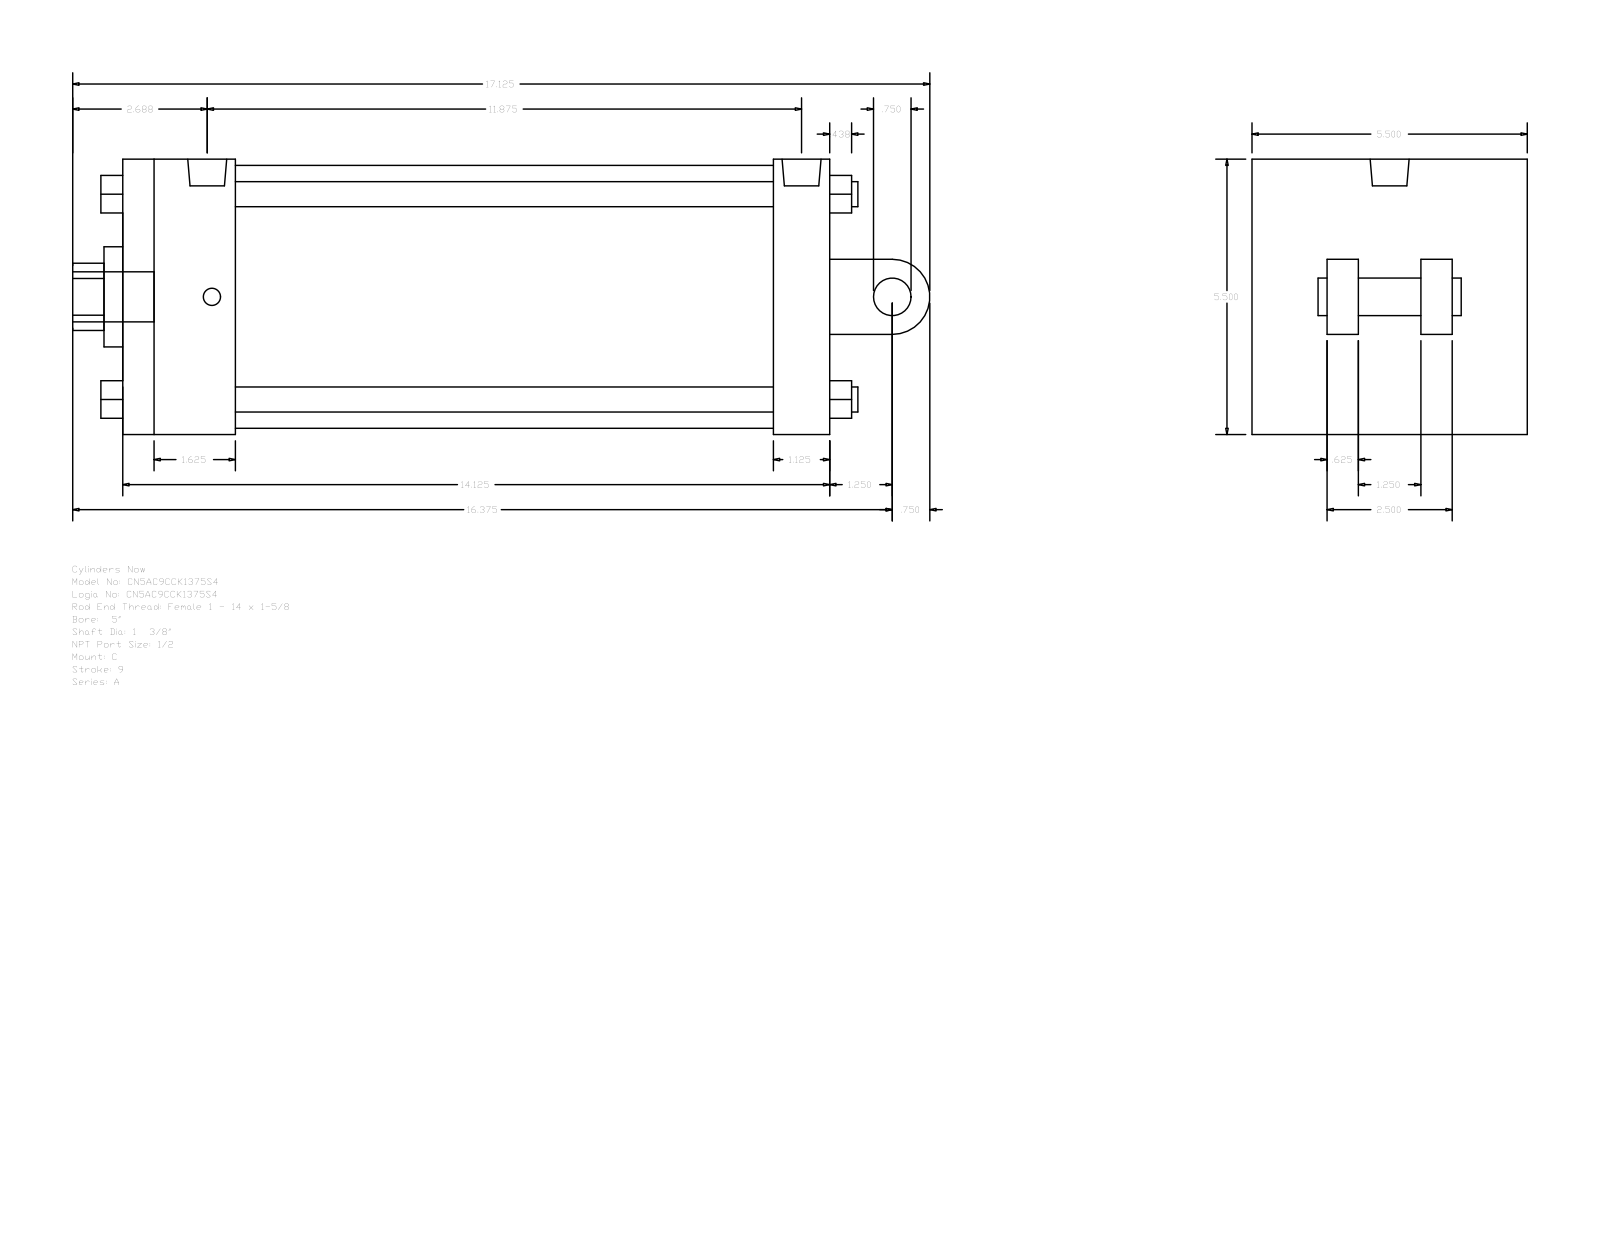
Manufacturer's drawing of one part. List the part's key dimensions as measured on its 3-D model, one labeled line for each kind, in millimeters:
Part name (STEP PRODUCT): A_C__0500_1.375
STEP written by: GSSL Pune (CONFIG_CONTROL_DESIGN)
Units: millimetres
Bodies: 0 solids, 135 faces (102 planar, 33 cylindrical, 0 other)
Overall size (bounding box): 434.98 × 139.7 × 139.7
Round holes (diameter × count): ⌀8.73 ×2, ⌀19.77 ×1, ⌀34.92 ×1, ⌀50.8 ×1, ⌀133.35 ×1
Round bosses / shafts (diameter × count): ⌀12.7 ×4, ⌀8.73 ×2, ⌀25.4 ×1, ⌀19.77 ×1, ⌀19.05 ×1
Partial cylindrical surfaces — rounded edges, fillets, slot ends (radius × count): R17.06 ×1, R19.05 ×1
Main face-to-face distances: 139.7, 358.78, 28.58, 57.15, 330.2, 273.05, 301.63, 38.1, 15.87, 101.6
Hole centre spacings: 2.39
